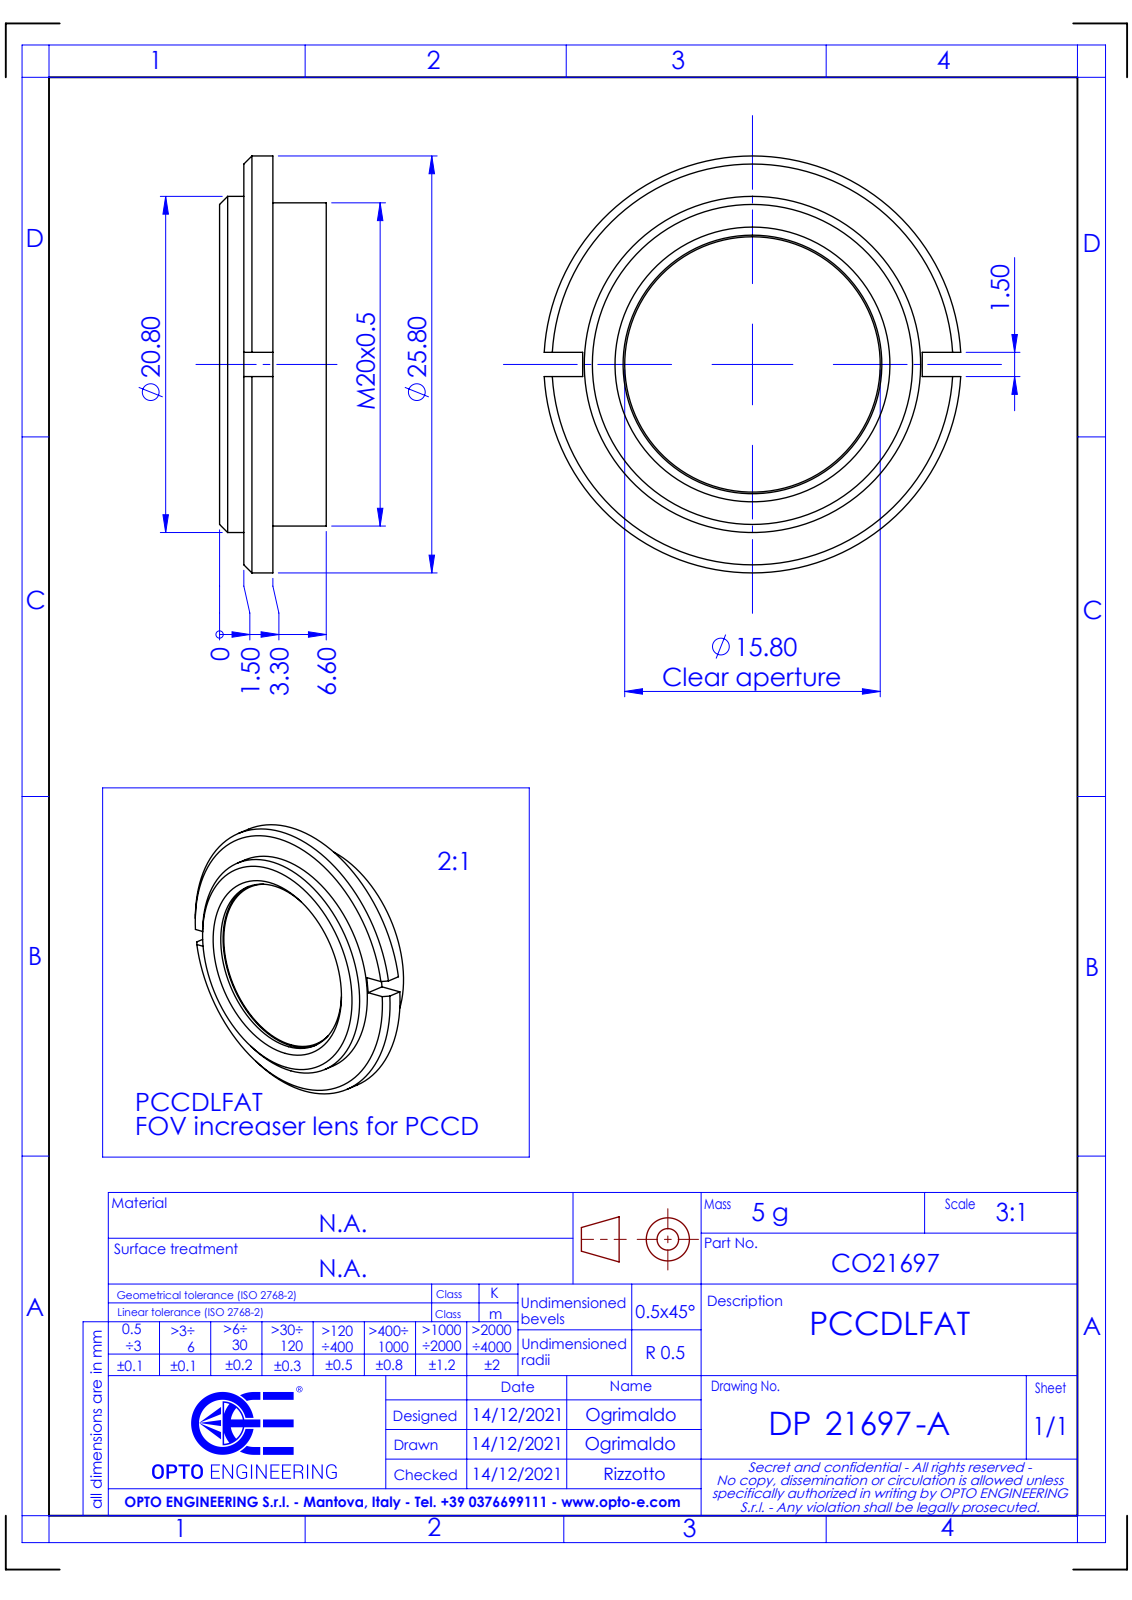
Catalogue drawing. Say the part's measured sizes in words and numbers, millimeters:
The part is named "DP21697-A_PCCDLFAT". Its 3-D file was written by "SolidWorks 2021 (CONFIG_CONTROL_DESIGN)". It is 0 solids with 38 faces: 12 planar, 13 cylindrical and 13 other. Overall it measures 25.8 by 25.76 by 6.6 millimeters. Round holes: 1 of diameter 16, 1 of diameter 17.8. Round bosses or shafts: 1 of diameter 25.8, 1 of diameter 20.8, 1 of diameter 20. The main face-to-face distances are 3.3, 1.8, 5.1, 1.5, 6.6, 0.8, 0.7, 2.5, 5.8, 21.
